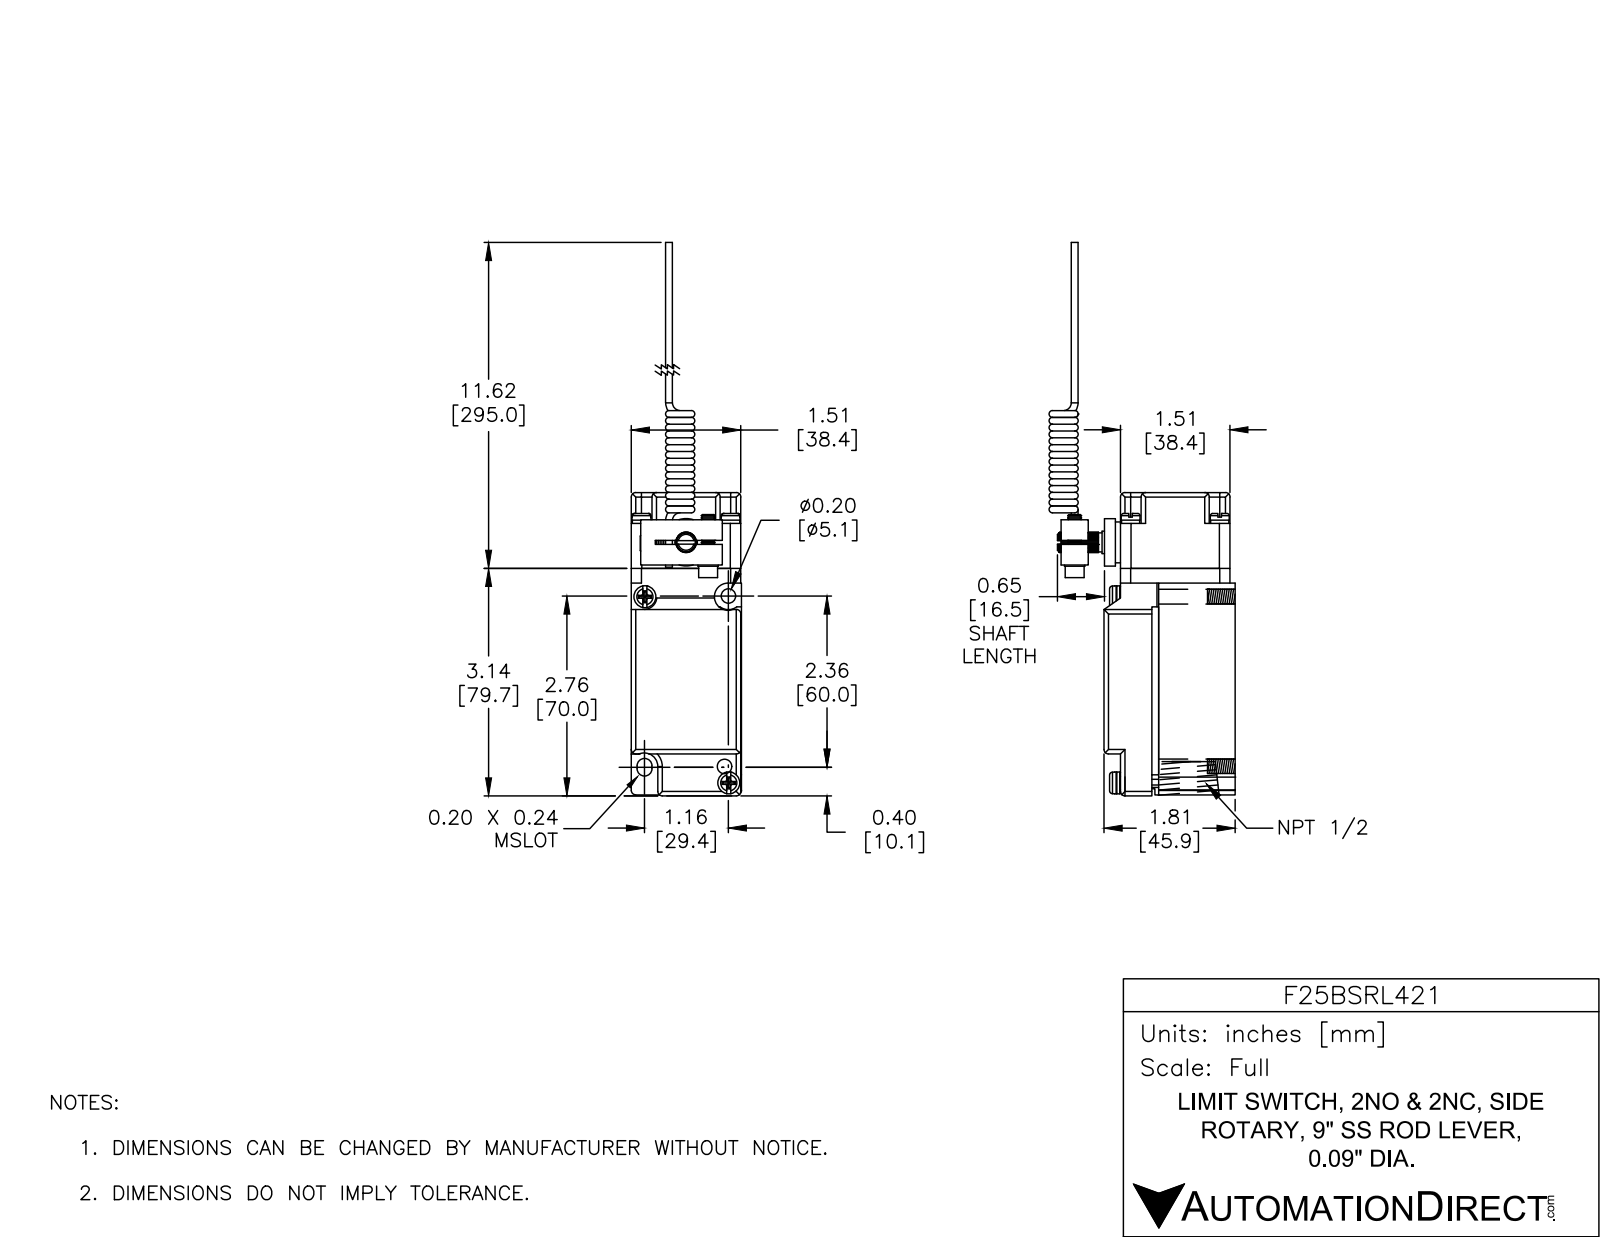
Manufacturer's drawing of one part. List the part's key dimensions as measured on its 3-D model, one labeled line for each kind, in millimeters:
Part name (STEP PRODUCT): F25BSRL421
STEP written by: SolidWorks 2018 (AUTOMOTIVE_DESIGN)
Units: millimetres
Bodies: 31 solids, 761 faces (440 planar, 155 cylindrical, 166 other)
Overall size (bounding box): 385.5 × 65.2 × 38.6
Volume: 171 600 mm³ · Surface area: 50 720 mm²
Round holes (diameter × count): ⌀4.5 ×4, ⌀4.8 ×3, ⌀5.1 ×3, ⌀3.4 ×1, ⌀5.2 ×1, ⌀5.3 ×1, ⌀7.2 ×1, ⌀14.7 ×1
Round bosses / shafts (diameter × count): ⌀6.6 ×4, ⌀6.4 ×4, ⌀7.7 ×2, ⌀7.6 ×2, ⌀16.6 ×1, ⌀14.4 ×1, ⌀7.8 ×1, ⌀7.1 ×1
Partial cylindrical surfaces — rounded edges, fillets, slot ends (radius × count): R1.6 ×29, R0.8 ×16, R0.4 ×8, R3.7 ×8, R3.6 ×4, R2.6 ×2, R4.8 ×2, R4.8 ×2
Main face-to-face distances: 2.4, 29.2, 26.8, 38.6, 16.8, 19.2, 45.9, 38.4, 5.8, 11
Hole centre spacings: 31.2, 31.2, 44.2, 71.5, 5.7, 6, 14.2, 21.1
